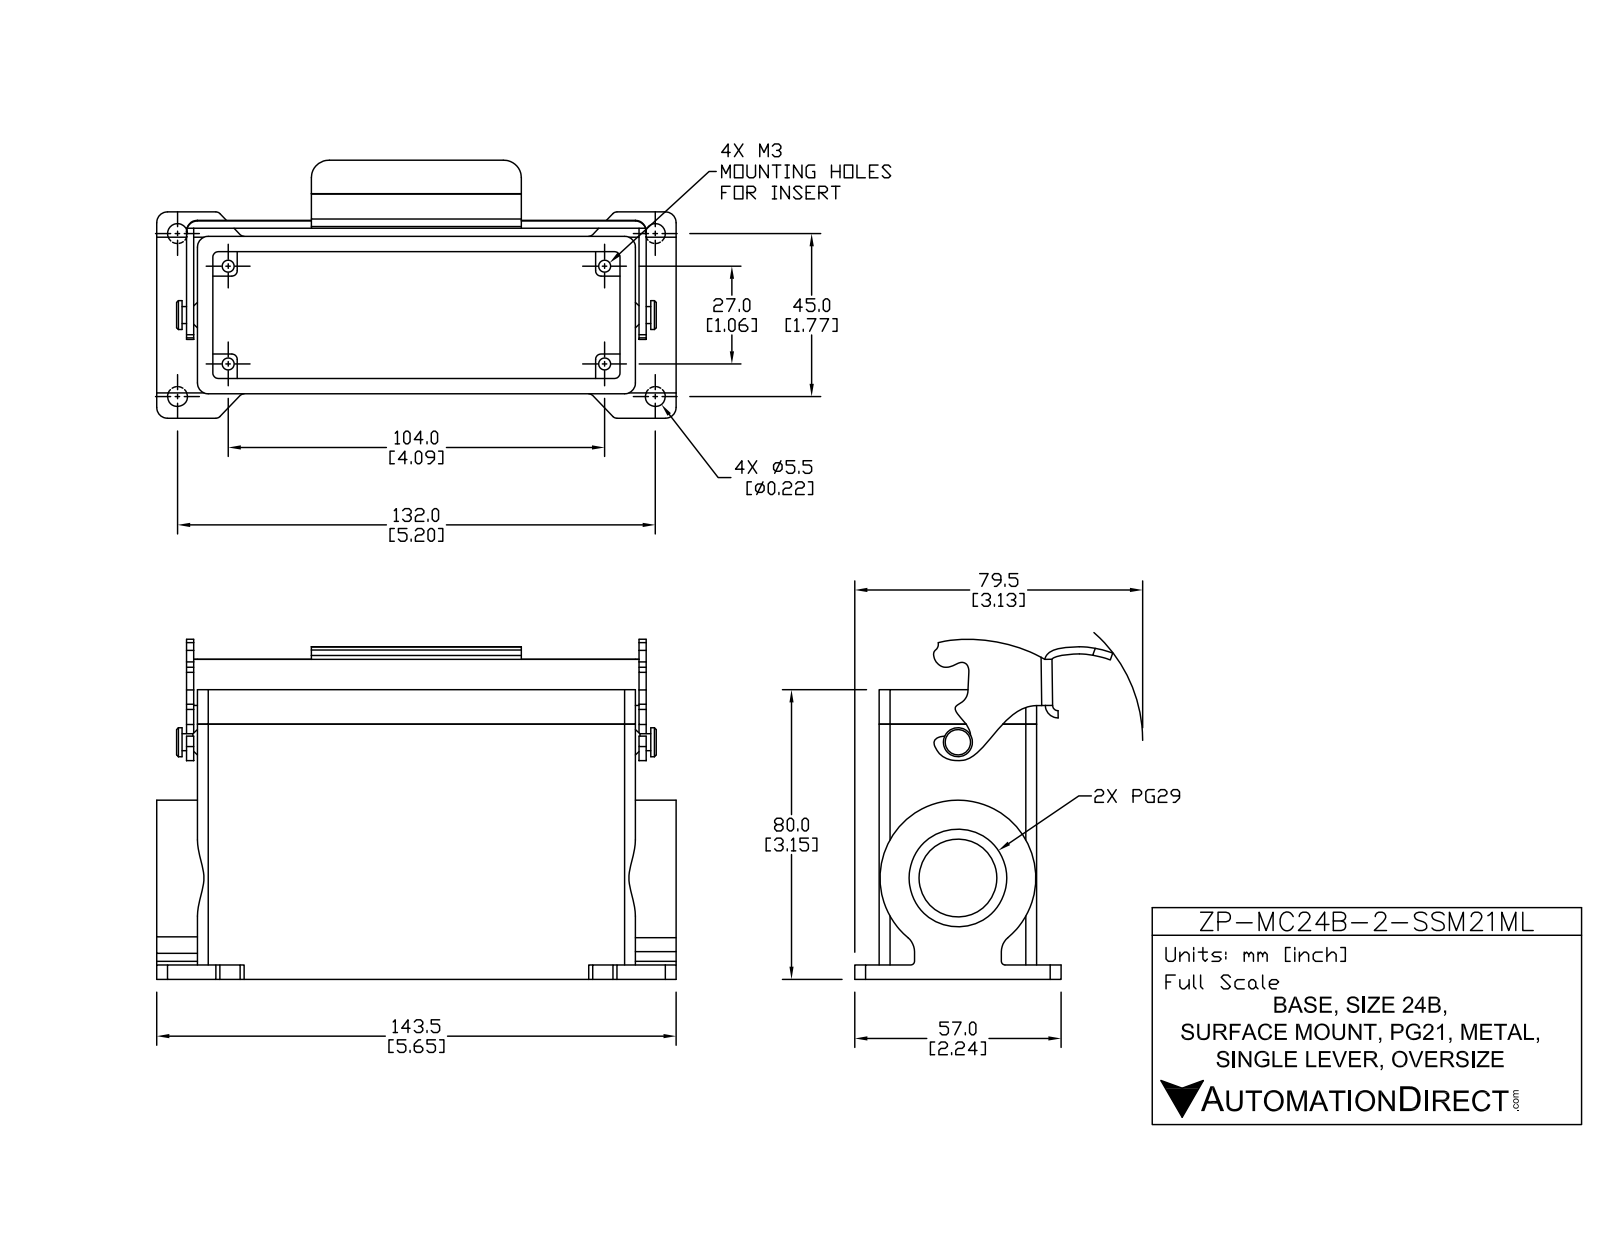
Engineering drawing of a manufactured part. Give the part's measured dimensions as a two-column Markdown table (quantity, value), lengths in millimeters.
| quantity | value |
| --- | --- |
| part name | ZP-MC24B-2-SSM21ML |
| STEP written by | SolidWorks 2011 (AUTOMOTIVE_DESIGN) |
| units | millimeters |
| bodies | 3 solids, 219 faces (97 planar, 118 cylindrical, 4 other) |
| overall size | 143.5 × 90.94 × 76.45 |
| volume | 154 246 mm³ |
| surface area | 77 073 mm² |
| round holes (diameter × count) | 3.3 × 4, 5.5 × 4, 21.5 × 1, 27 × 1 |
| round bosses / shafts (diameter × count) | 8 × 1, 4.67 × 1 |
| partial cylindrical surfaces (radius × count) | 1.5 × 16, 0.5 × 13, 3 × 9, 1 × 4, 2 × 3, 4 × 3, 5 × 3, 6 × 2 |
| main face-to-face distances | 4.25, 39.25, 43.5, 35, 2.5, 1.15, 6.75, 11, 116.75, 70.5 |
| hole center spacings | 16.64, 38.63, 118.34, 123.37, 27, 45, 104, 107.45 |
